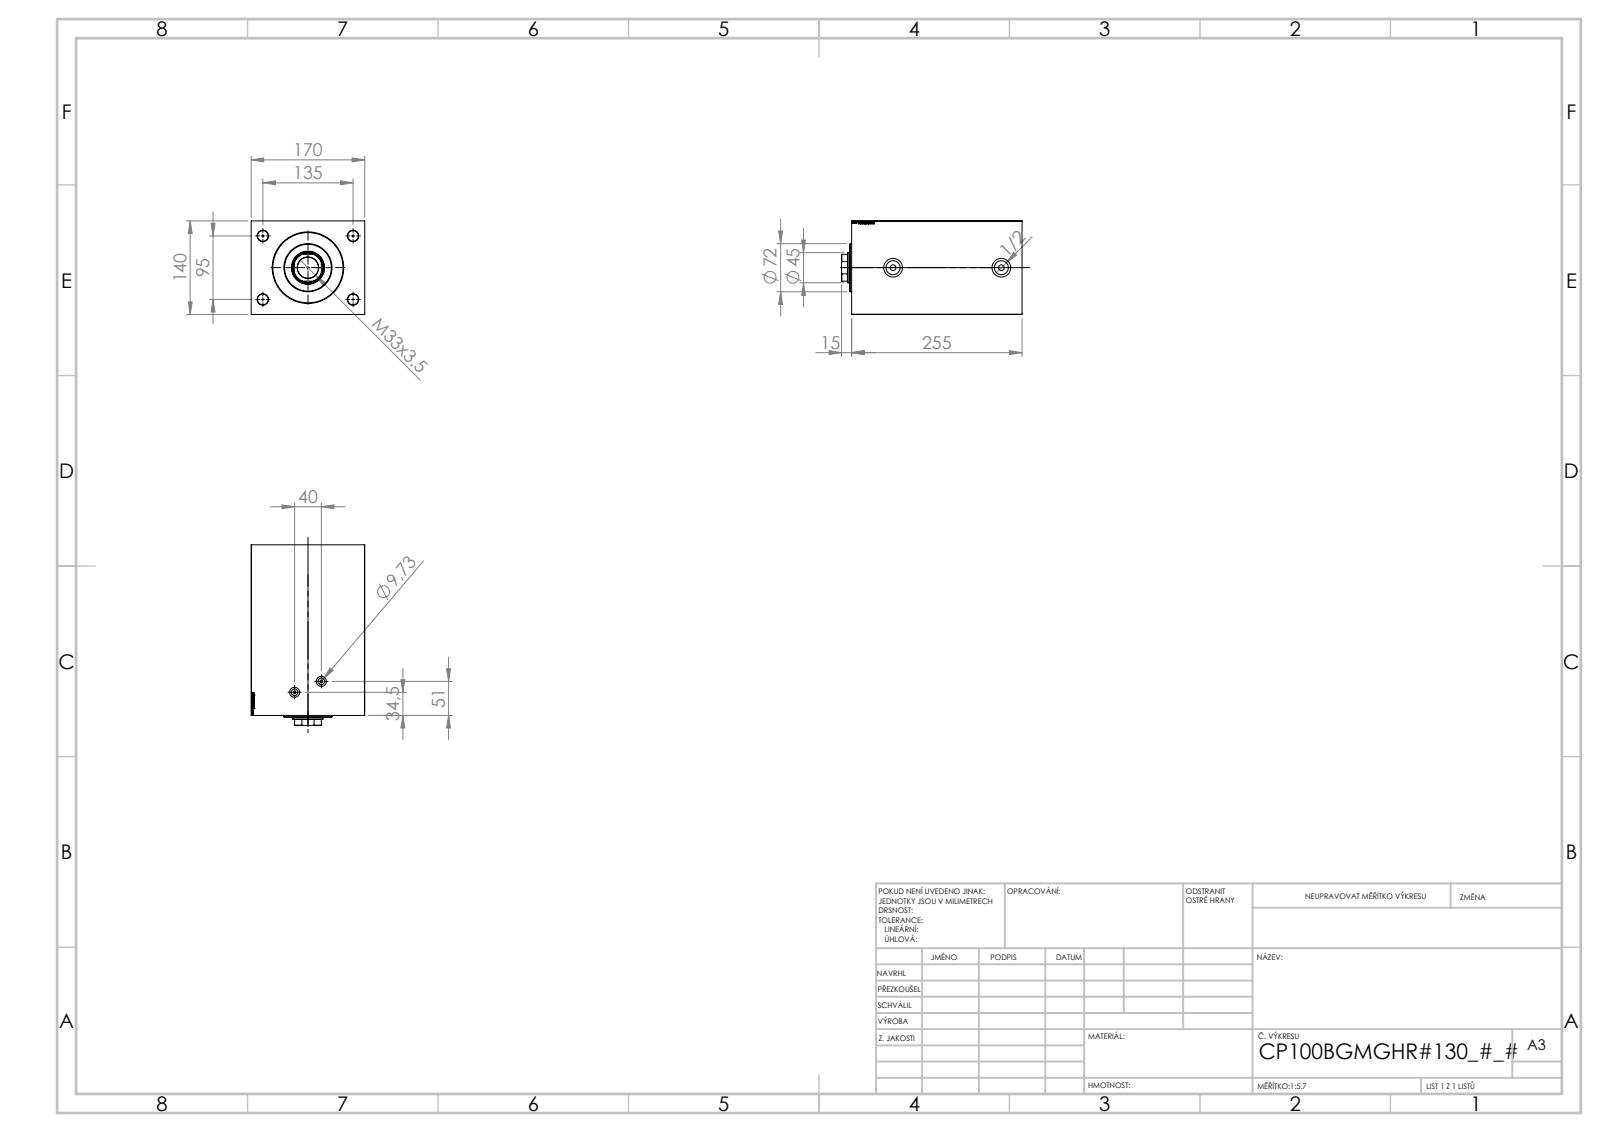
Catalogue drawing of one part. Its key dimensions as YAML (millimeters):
part_name: "V450CP_B; V450CP_VC_B; V450CP_B_VCP"
step_written_by: "SolidWorks 2019 (CONFIG_CONTROL_DESIGN)"
units: millimeters
bodies: {solids: 3, faces: 904, planar: 406, cylindrical: 68, other: 430}
overall_size: [270, 170, 140]
volume: 5188000
surface_area: 399429
round_holes:
  - {diameter: 16, count: 4}
  - {diameter: 4, count: 2}
  - {diameter: 8.5, count: 2}
  - {diameter: 9.73, count: 2}
  - {diameter: 15, count: 2}
  - {diameter: 20.96, count: 2}
  - {diameter: 28, count: 2}
  - {diameter: 31.5, count: 1}
  - {diameter: 45, count: 1}
  - {diameter: 48.5, count: 1}
  - {diameter: 49.5, count: 1}
  - {diameter: 100, count: 1}
round_bosses_or_shafts:
  - {diameter: 72, count: 1}
partial_cylinders:
  - {radius: 22, count: 1}
face_to_face_distances: [140, 170, 255, 26, 229, 186, 160, 69, 56, 30]
hole_center_spacings: [82.54, 95, 135, 165.08, 43.19, 162]
